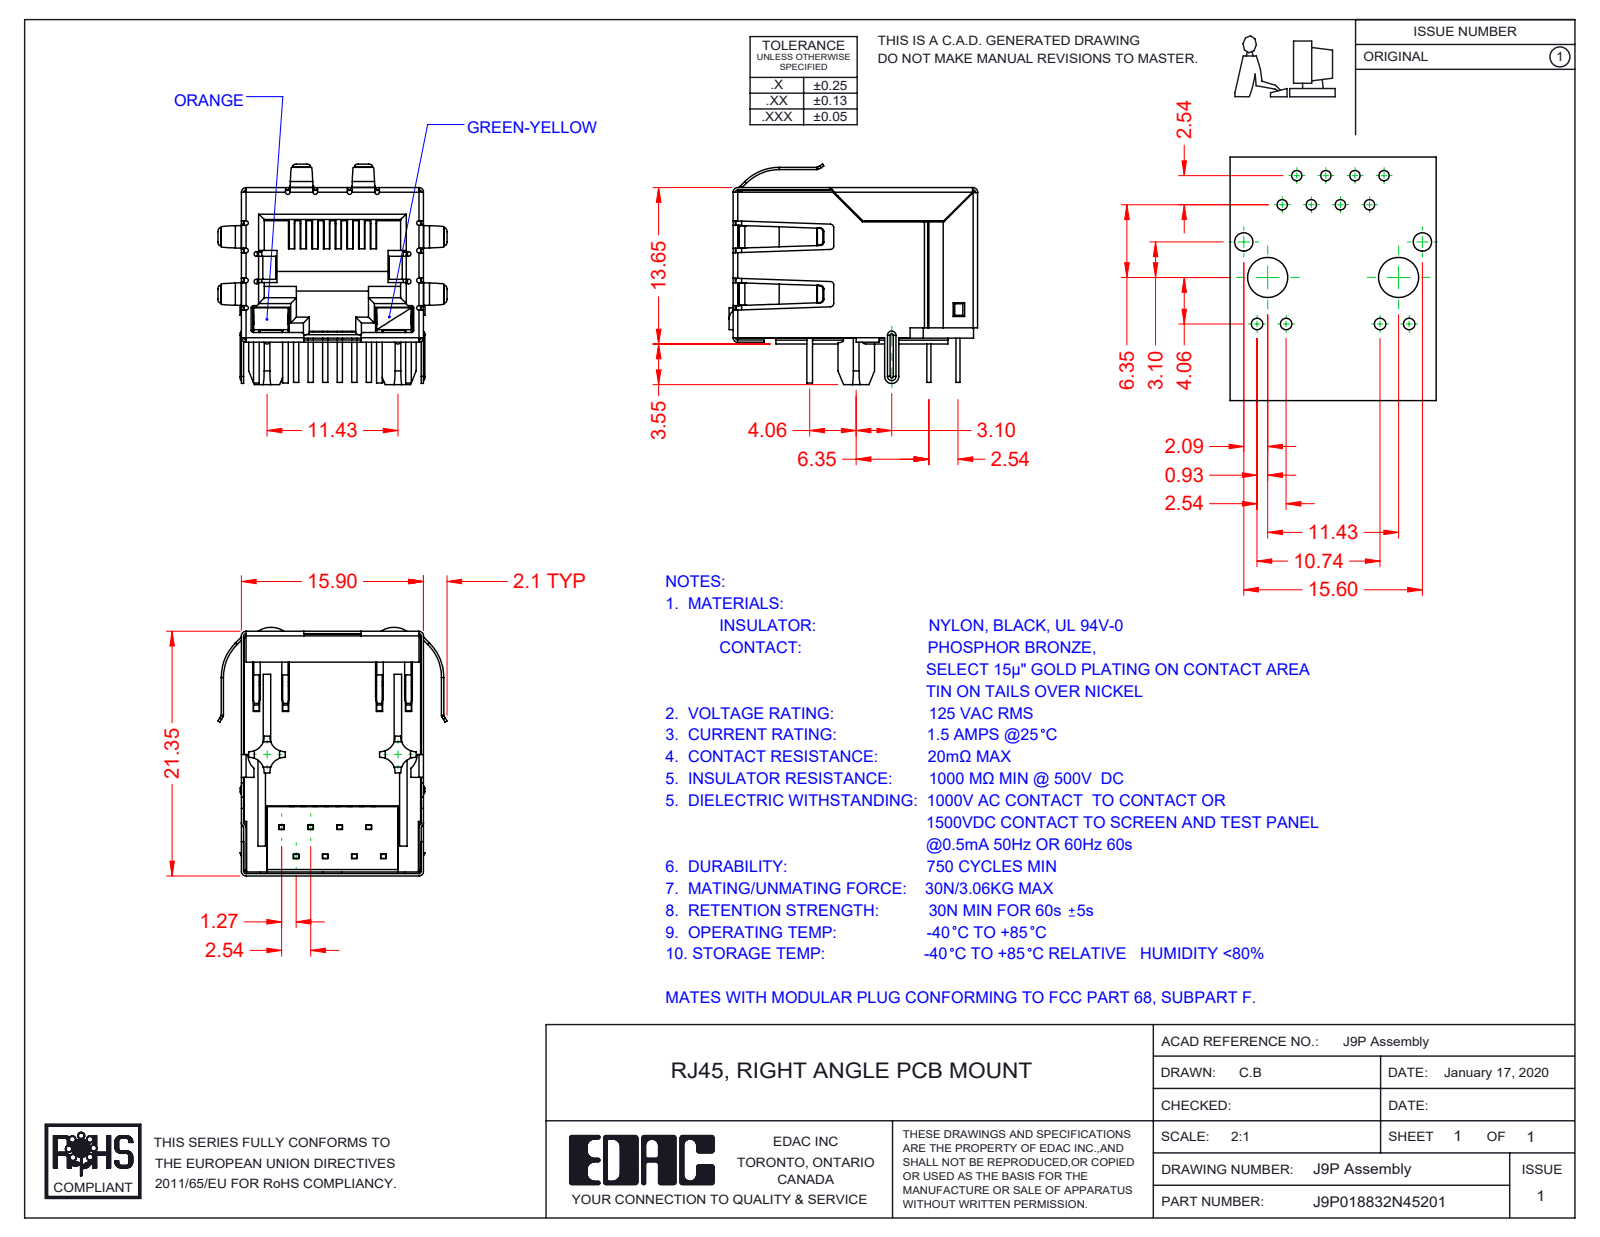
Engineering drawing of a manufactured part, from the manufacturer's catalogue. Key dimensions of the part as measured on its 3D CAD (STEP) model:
Part name (STEP PRODUCT): J9P018832N45202; 9P-LED LED RH_5-Green-Yellow; 9P-LED LED LH_4-Orange; 9P-LED Assembly (+4 more)
STEP written by: SolidWorks 2016 (CONFIG_CONTROL_DESIGN)
Units: millimetres
Bodies: 13 solids, 1474 faces (1042 planar, 338 cylindrical, 94 other)
Overall size (bounding box): 21.7 × 20 × 19.25
Volume: 2 687 mm³ · Surface area: 7 515 mm²
Partial cylindrical surfaces — rounded edges, fillets, slot ends (radius × count): R0.2 ×39, R0.5 ×22, R0.3 ×20, R0.4 ×16, R1.3 ×8, R0.23 ×5, R0.11 ×4, R0.31 ×4
Main face-to-face distances: 15.45, 15.7, 15.65, 0.35, 0.54, 15.5, 12.36, 0.6, 1.4, 0.59
